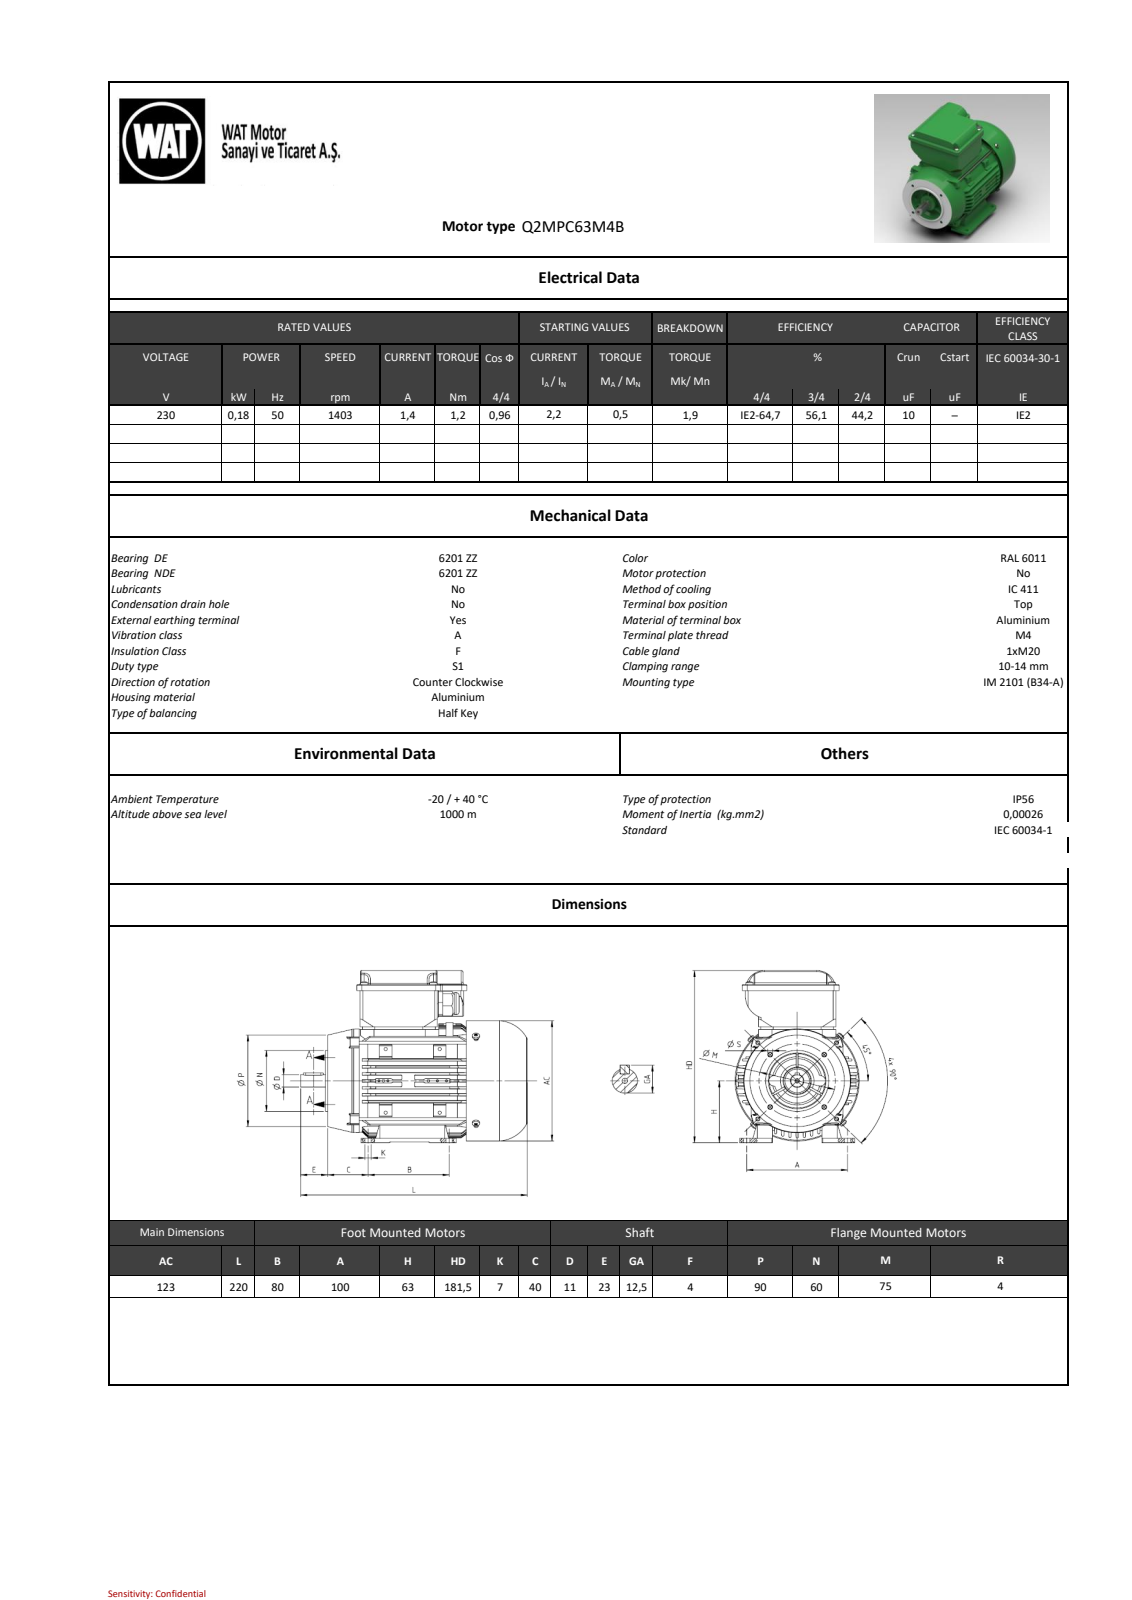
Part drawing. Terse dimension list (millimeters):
name: BY6434017xx_004-TK_QM63-80; BY6424130xx_004-TKK_QM63-80; BY6424111xx_004-MOTOR_KAPAGI_QS63FC_ISLEME; BY6423003xx_006-FAN_KAPAGI_QS63 (+8 more)
written by: SIEMENS PLM Software NX2206.8101 (AUTOMOTIVE_DESIGN)
unit: mm
bodies: 36 solids, 2244 faces (1155 planar, 801 cylindrical, 288 other)
size: 219.47 × 181.5 × 123
volume: 592 191 mm³; area: 421 574 mm²
holes: 10× ⌀3.65, 9× ⌀3.3, 8× ⌀4.5, 6× ⌀2.5, 4× ⌀3.5, 4× ⌀3.8, 4× ⌀4.2, 4× ⌀4.65, 4× ⌀4.8, 3× ⌀3, 2× ⌀7, 1× ⌀5
bosses: 8× ⌀8, 8× ⌀4, 8× ⌀3, 1× ⌀123, 1× ⌀121, 1× ⌀99, 1× ⌀70, 1× ⌀60
rounds: 212× R0.5, 126× R1, 60× R2, 20× R2.5, 11× R4, 10× R5, 9× R3, 9× R5.5
face distances: 3, 1.5, 1, 4, 4.5, 7.02, 27.96, 7, 2.5, 10.5
hole spacings: 77, 55, 54, 66.12, 54.45, 0.61, 37.5, 62.8
